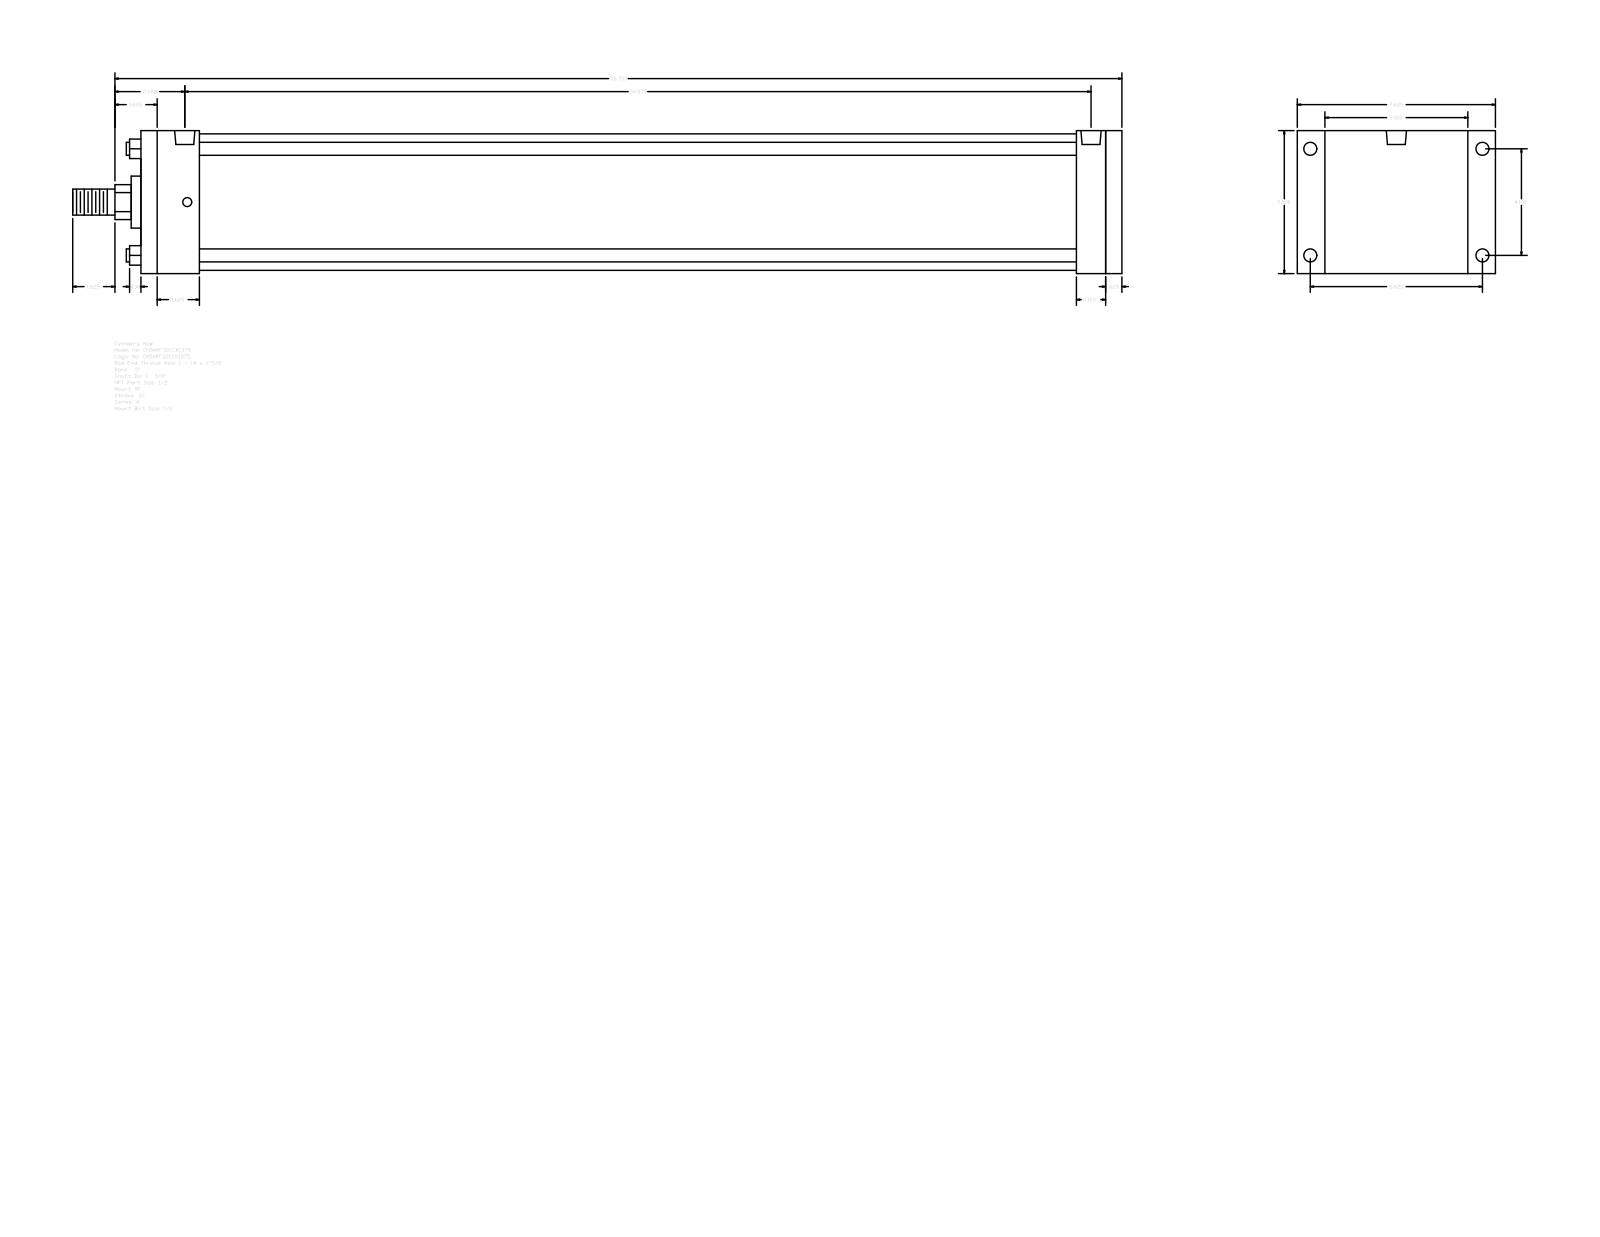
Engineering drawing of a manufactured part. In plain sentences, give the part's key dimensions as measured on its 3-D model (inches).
The part is named "A_RF__0500_1.375". Its 3-D file was written by "GSSL Pune (CONFIG_CONTROL_DESIGN)". It is 0 solids with 92 faces: 64 planar, 28 cylindrical and 0 other. Overall it measures 40.375 by 7.625 by 5.5 inches. Round holes: 4 of diameter 0.344, 4 of diameter 0.5, 2 of diameter 0.778. Round bosses or shafts: 4 of diameter 0.5, 1 of diameter 5.25, 1 of diameter 2, 1 of diameter 1.375, 1 of diameter 1. Partial cylindrical surfaces (rounded edges, fillets, slot ends): 1 of radius 0.672. The main face-to-face distances are 5.5, 37.75, 37.125, 0.625, 2.25, 1.125, 34.875, 35.5, 36, 33.75. The hole center spacings are 0.094, 4.1, 6.625, 7.791, 34.687, 34.781, 34.875.
